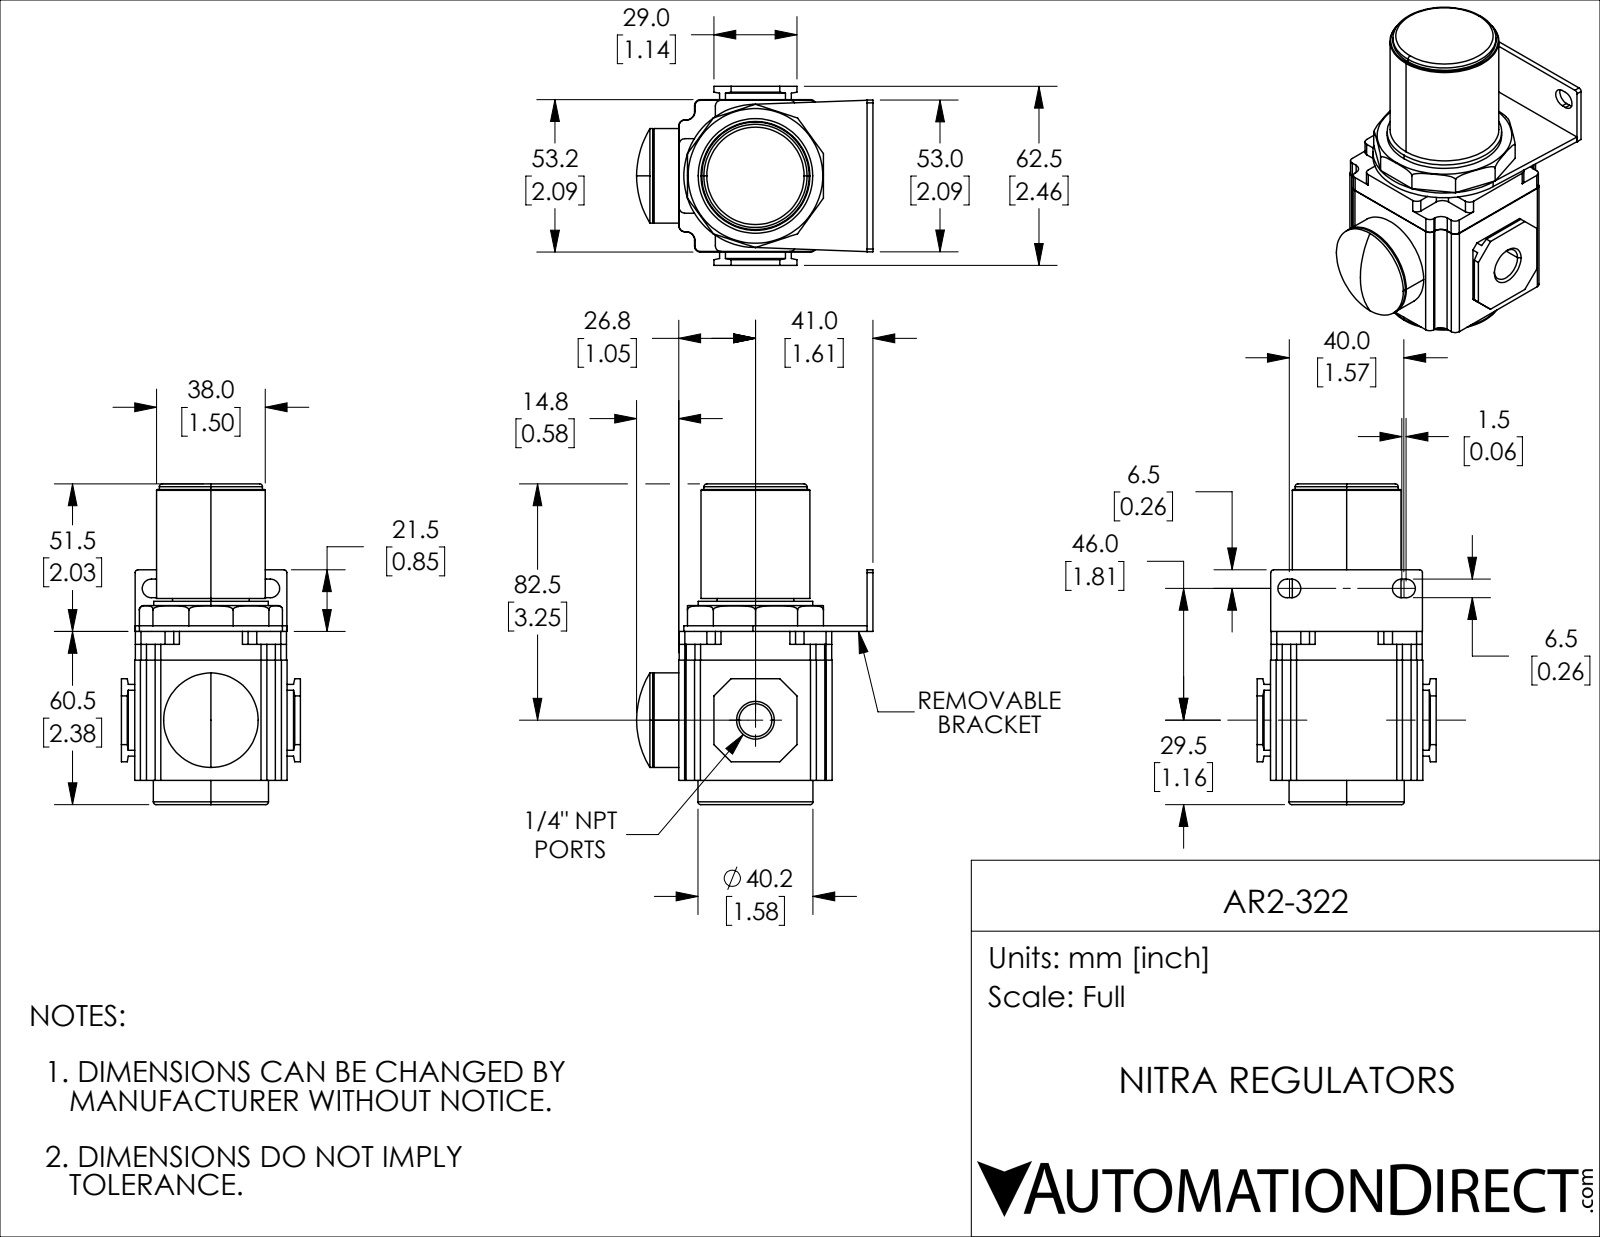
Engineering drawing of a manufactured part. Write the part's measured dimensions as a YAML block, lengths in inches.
part_name: "AR2-322"
step_written_by: "SolidWorks 2019 (CONFIG_CONTROL_DESIGN)"
units: inches
bodies: {solids: 1, faces: 188, planar: 111, cylindrical: 61, other: 16}
overall_size: [4.409, 3.248, 2.461]
volume: 14.09
surface_area: 50.16
round_holes:
  - {diameter: 0.451, count: 1}
round_bosses_or_shafts:
  - {diameter: 1.583, count: 1}
  - {diameter: 1.575, count: 1}
  - {diameter: 1.496, count: 1}
  - {diameter: 1.417, count: 1}
  - {diameter: 1.299, count: 1}
  - {diameter: 1.054, count: 1}
partial_cylinders:
  - {radius: 0.079, count: 24}
  - {radius: 0.118, count: 12}
  - {radius: 0.128, count: 4}
  - {radius: 0.039, count: 2}
  - {radius: 0.984, count: 1}
face_to_face_distances: [2.461, 0.079, 0.335, 2.126, 2.047, 0.183, 2.278, 0.561, 2.382, 2.205]
